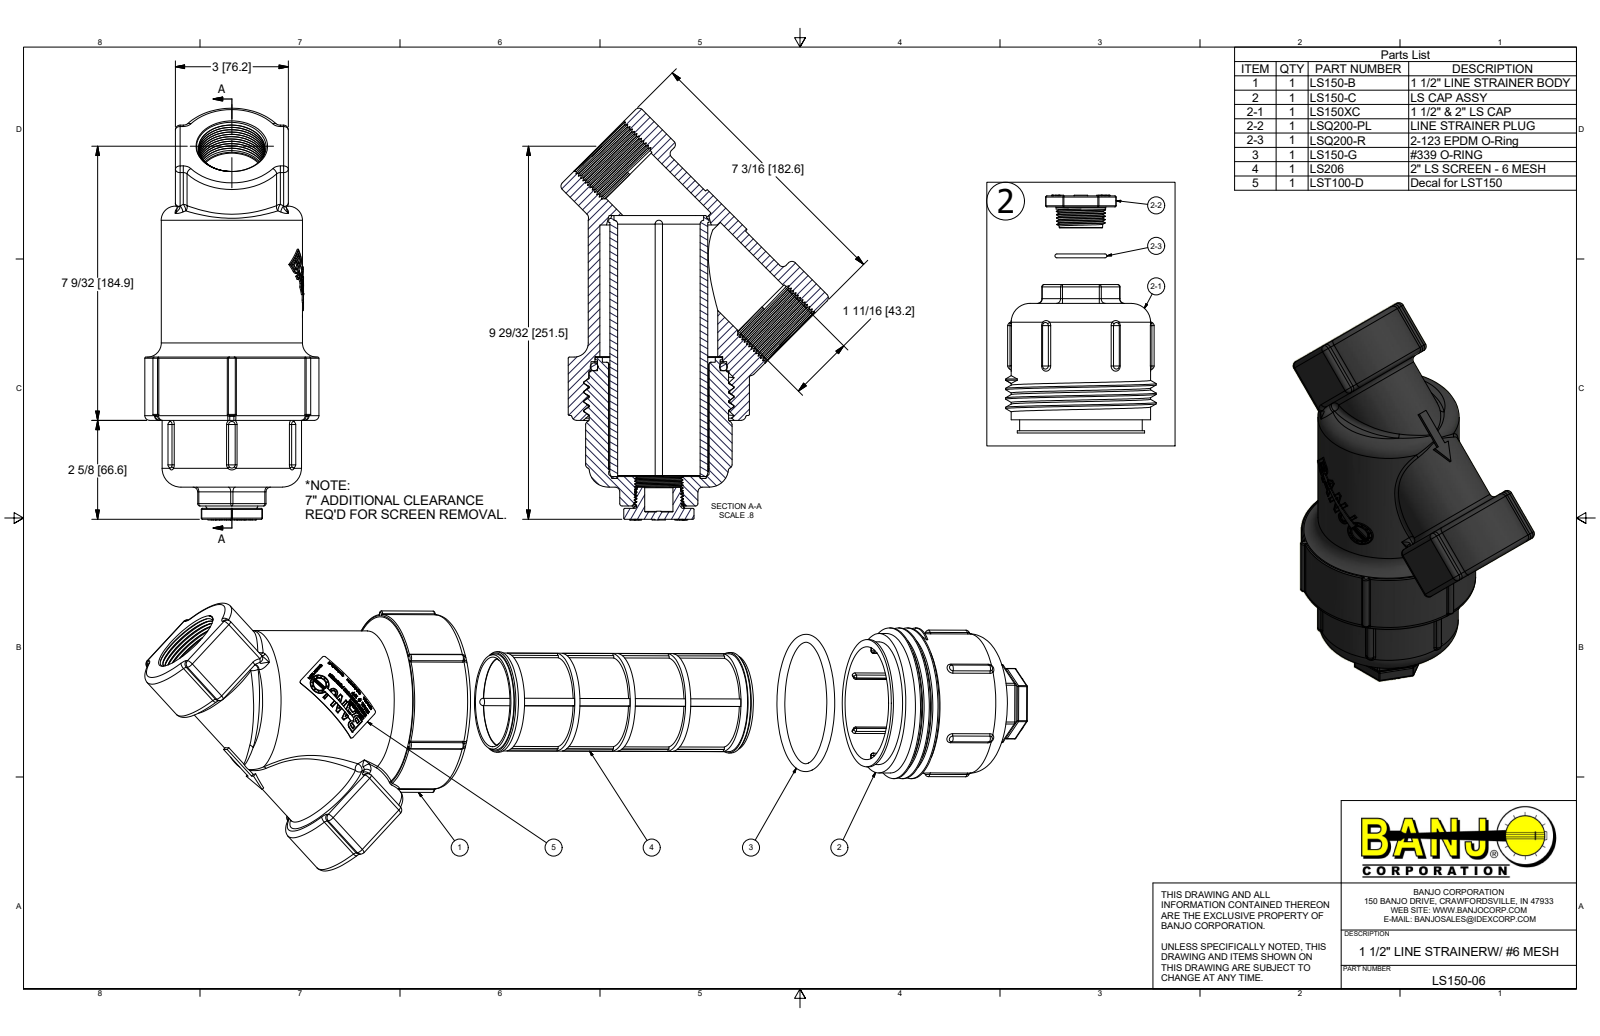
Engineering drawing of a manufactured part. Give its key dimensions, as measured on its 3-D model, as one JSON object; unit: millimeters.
{"part_name": "LS150-06; LS150-B; LS150-C; LS150XC (+5 more)", "step_written_by": "Autodesk Inventor 2018 (AUTOMOTIVE_DESIGN)", "units": "millimeters", "bodies": {"solids": 7, "faces": 3244, "planar": 1476, "cylindrical": 513, "other": 1255}, "overall_size": [548.4, 180.4, 117.5], "volume_mm3": 981900, "surface_area_mm2": 423200, "round_holes": [[43.2, 2], [44.7, 2], [8.3, 1], [11.5, 1], [11.7, 1], [16.3, 1], [19.1, 1], [55.6, 1], [59.7, 1], [76.2, 1], [79.5, 1], [86.2, 1]], "round_bosses_or_shafts": [[117.5, 1], [101.6, 1], [95.3, 1], [94, 1], [85.9, 1], [82.7, 1], [67.7, 1], [66, 1]], "partial_cylinders_radius": [[1.5, 50], [3.2, 35], [0.8, 30], [2.4, 12], [2.5, 4], [3, 4], [0.7, 2], [1, 2]], "face_to_face_distances": [76.2, 182.6, 36.7, 176, 34, 5.1, 3.2, 37.9, 138.1, 71.4], "hole_center_spacings": [47.9]}
